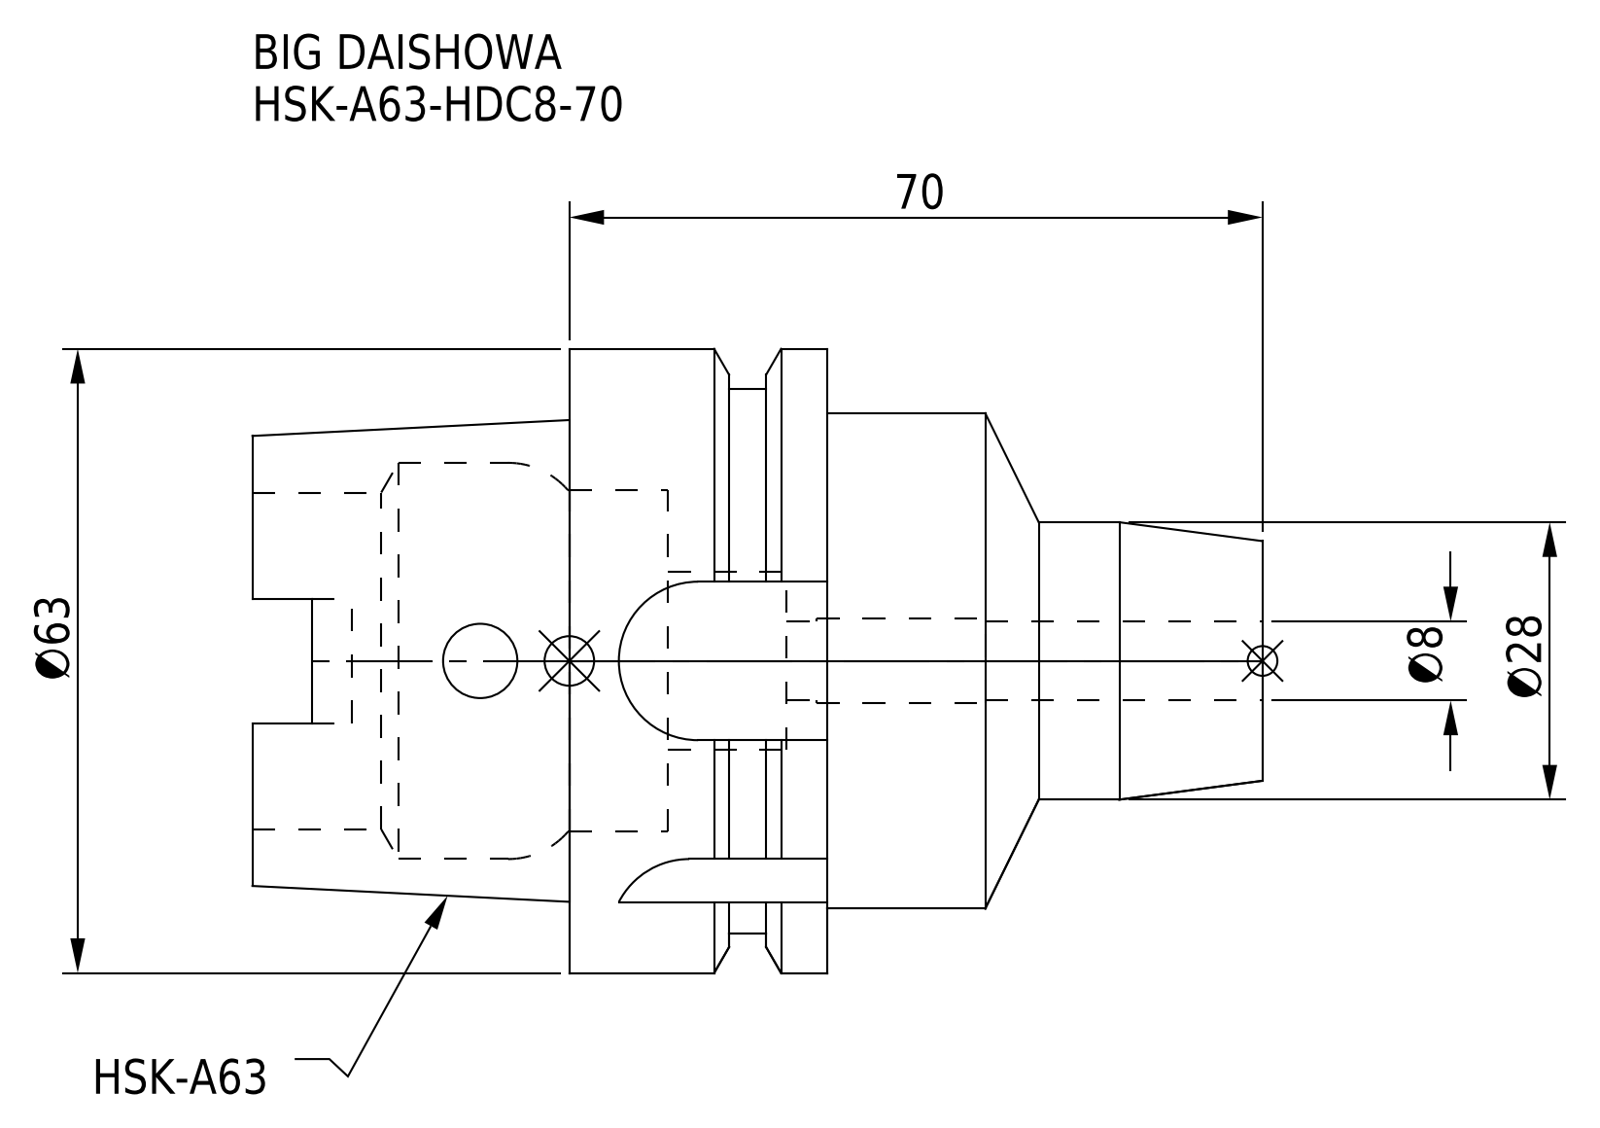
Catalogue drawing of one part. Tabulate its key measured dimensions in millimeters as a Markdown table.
| quantity | value |
| --- | --- |
| part name | HSK-A63-HDC8-70 |
| STEP written by | CREO PARAMETRIC BY PTC INC, 2016380 (AUTOMOTIVE_DESIGN) |
| units | millimeters |
| bodies | 1 solid, 95 faces (38 planar, 39 cylindrical, 18 other) |
| overall size | 102 × 63 × 63 |
| volume | 130 097 mm³ |
| surface area | 27 886 mm² |
| round holes (diameter × count) | 7.5 × 1, 8 × 1, 8.5 × 1, 18 × 1, 34 × 1, 34.5 × 1, 40 × 1 |
| round bosses / shafts (diameter × count) | 63 × 1, 55 × 1, 50 × 1, 28 × 1 |
| partial cylindrical surfaces (radius × count) | 2.88 × 4, 8 × 4 |
| main face-to-face distances | 26, 16.05, 9.95, 58, 41.95, 32, 44, 60.05, 70, 102 |
